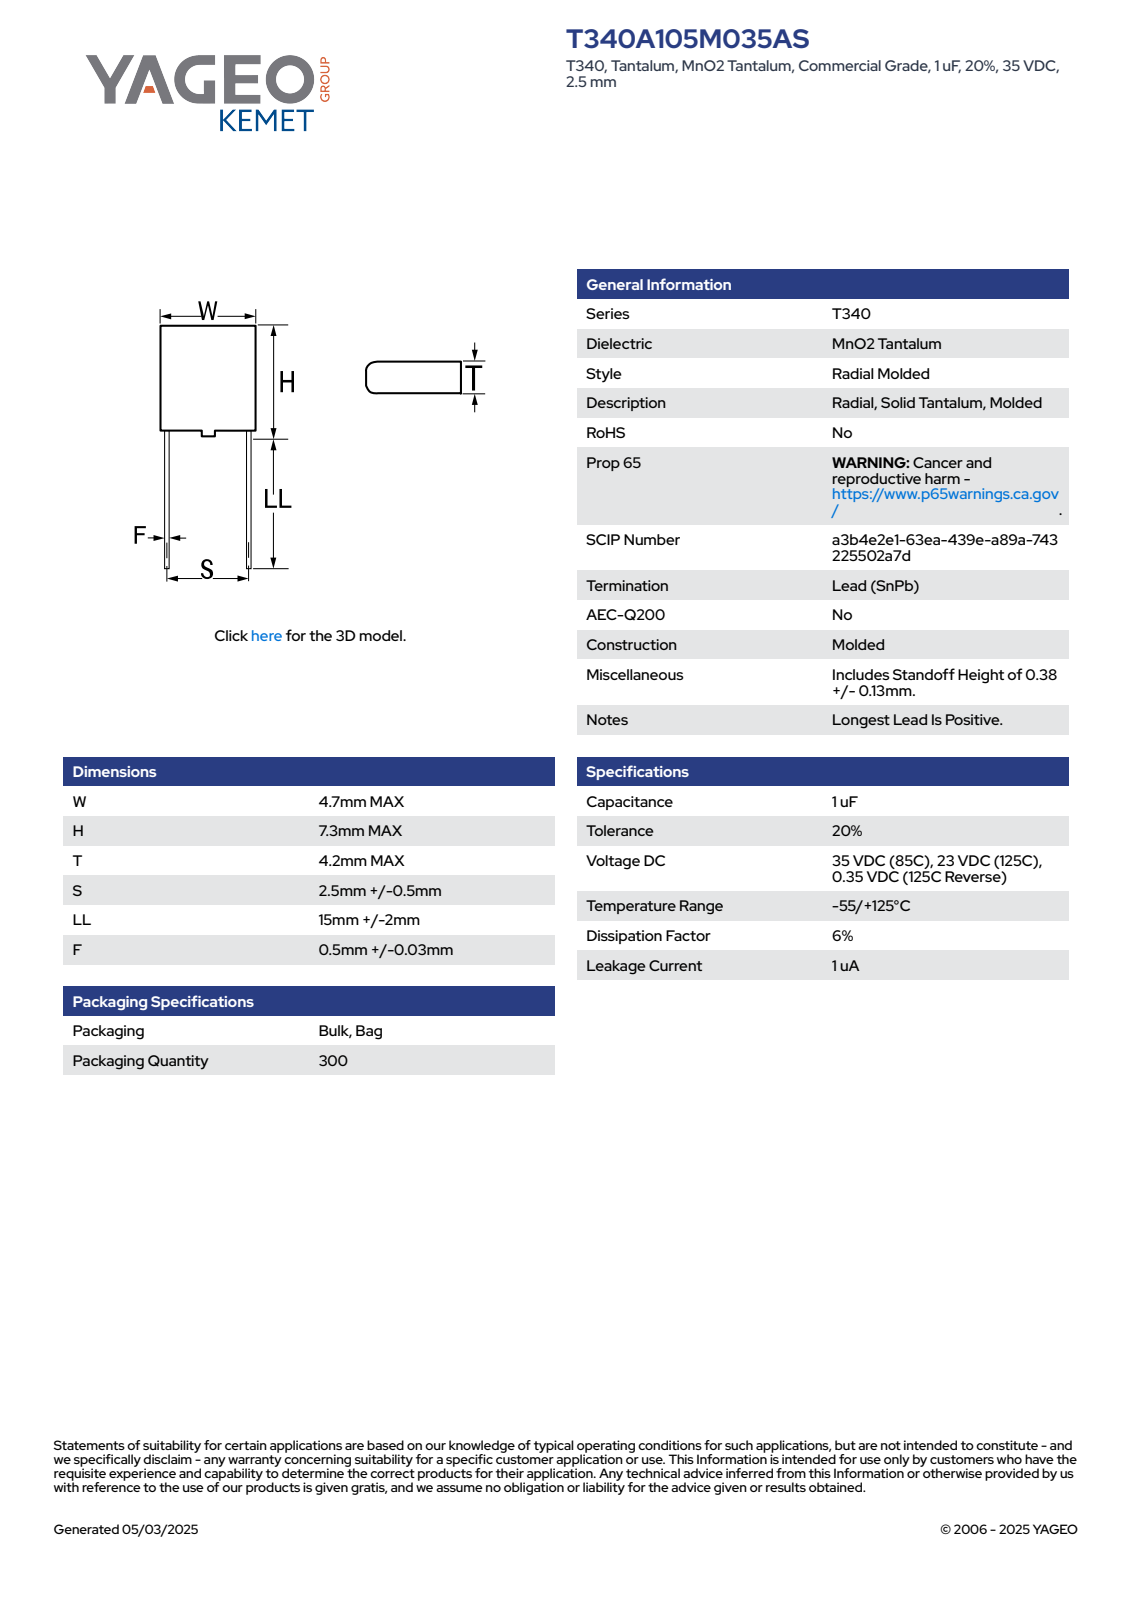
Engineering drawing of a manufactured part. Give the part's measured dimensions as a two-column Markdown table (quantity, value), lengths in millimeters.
| quantity | value |
| --- | --- |
| part name | CTR_T340A_W4.7H7.3T4.2S2.5LL17F0.53G0.51 |
| STEP written by | SolidWorks 2014 (AUTOMOTIVE_DESIGN) |
| units | millimeters |
| bodies | 4 solids, 75 faces (69 planar, 6 cylindrical, 0 other) |
| overall size | 24.3 × 4.7 × 4.21 |
| volume | 142 mm³ |
| surface area | 220 mm² |
| round bosses / shafts (diameter × count) | 0.53 × 2 |
| partial cylindrical surfaces (radius × count) | 1 × 2 |
| main face-to-face distances | 4.2, 4.7, 6.79, 0.51, 7.3, 1.6, 3.1, 1.5, 17, 17.51 |
